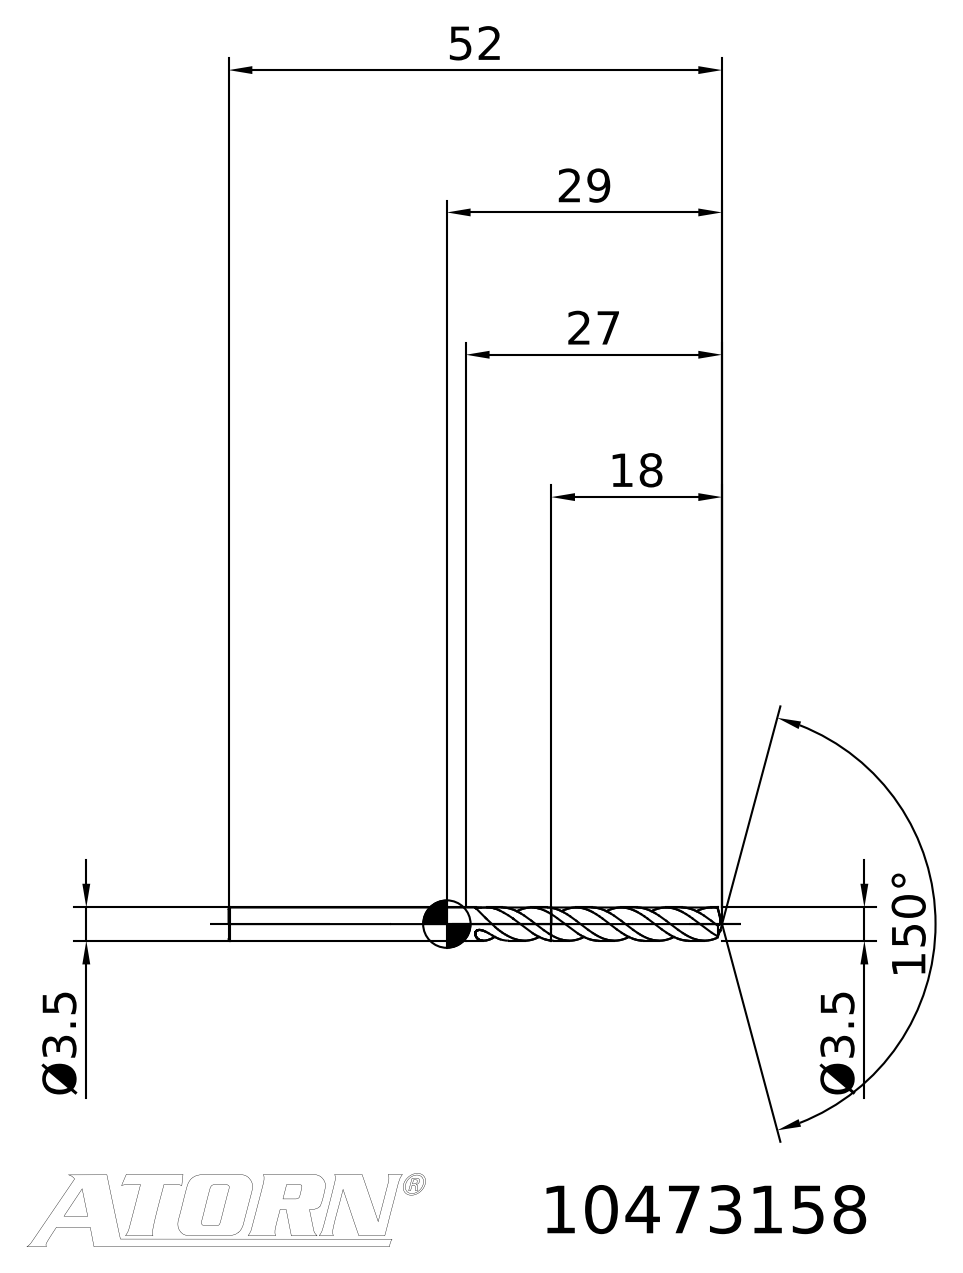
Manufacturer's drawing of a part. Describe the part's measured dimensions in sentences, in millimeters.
Its 3-D file was written by "TDM (AUTOMOTIVE_DESIGN)". It is 2 solids with 37 faces: 3 planar, 0 cylindrical and 34 other. Overall it measures 52 by 4.35 by 4.11 millimeters. Its volume is 375 cubic millimeters and its surface area 639 square millimeters. The main face-to-face distances are 34.
